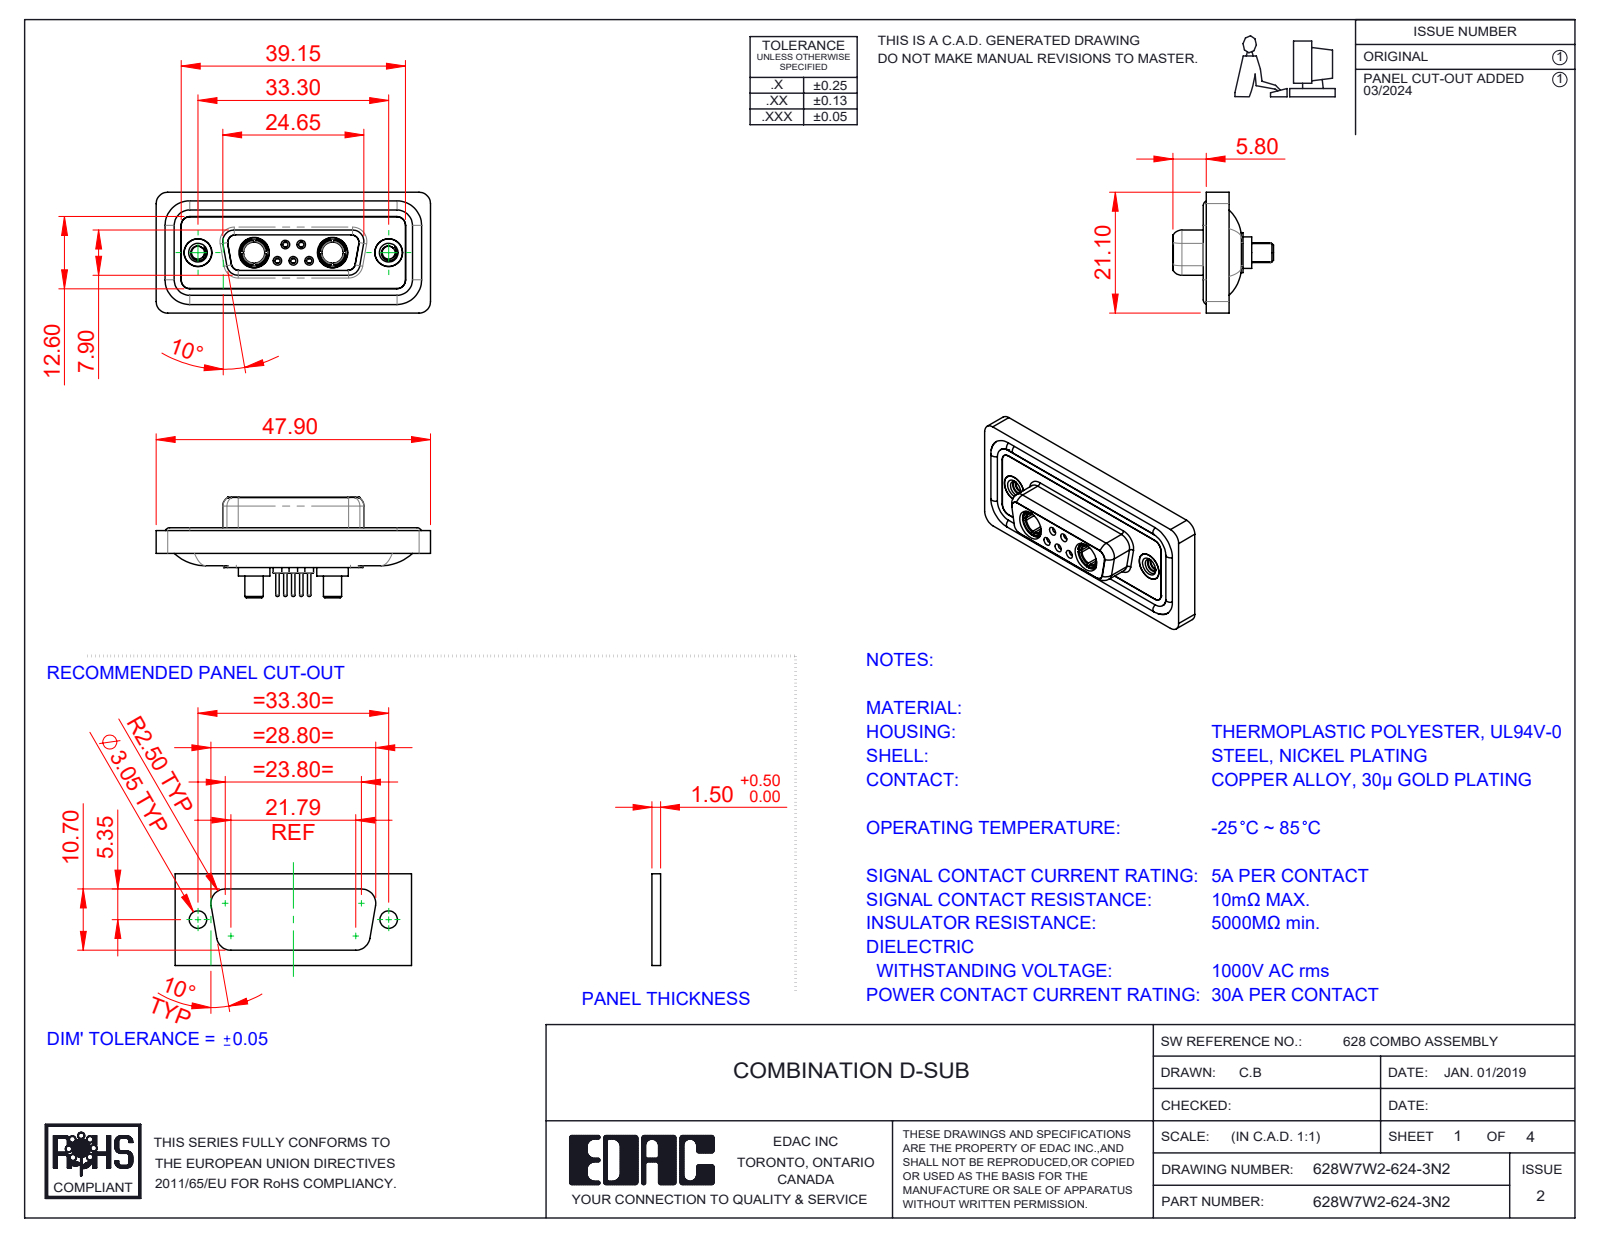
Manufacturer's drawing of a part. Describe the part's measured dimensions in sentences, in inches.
The part is named "Power Socket_30A S; 628Combo Waterproof Housing_15 Contacts; 628Combo Shell Rear_15 Contacts; 628Combo Contact Row 2_24 (+5 more)". Its 3-D file was written by "SolidWorks 2023 (CONFIG_CONTROL_DESIGN)". It is 16 solids with 809 faces: 238 planar, 329 cylindrical and 242 other. Overall it measures 1.886 by 0.831 by 0.691 inches. Its volume is 0.372 cubic inches and its surface area 15.34 square inches. Round holes: 5 of diameter 0.035, 5 of diameter 0.043, 5 of diameter 0.059, 5 of diameter 0.079, 4 of diameter 0.191, 3 of diameter 0.063, 2 of diameter 0.067, 2 of diameter 0.089, 2 of diameter 0.146, 2 of diameter 0.157, 2 of diameter 0.159, 2 of diameter 0.197. Round bosses or shafts: 6 of diameter 0.063, 5 of diameter 0.087, 5 of diameter 0.024, 2 of diameter 0.217, 2 of diameter 0.205, 2 of diameter 0.195, 2 of diameter 0.195, 2 of diameter 0.189. Partial cylindrical surfaces (rounded edges, fillets, slot ends): 22 of radius 0.059, 20 of radius 0.079, 12 of radius 0.053, 8 of radius 0.063, 4 of radius 0.01, 4 of radius 0.02, 4 of radius 0.024, 4 of radius 0.026. The main face-to-face distances are 0.016, 0.071, 0.063, 0.02, 0.114, 0.293, 0.043, 0.222, 0.26, 0.278. The hole center spacings are 0.124, 0.109, 0.386, 0.925, 0.17, 0.17, 0.198, 0.198.
